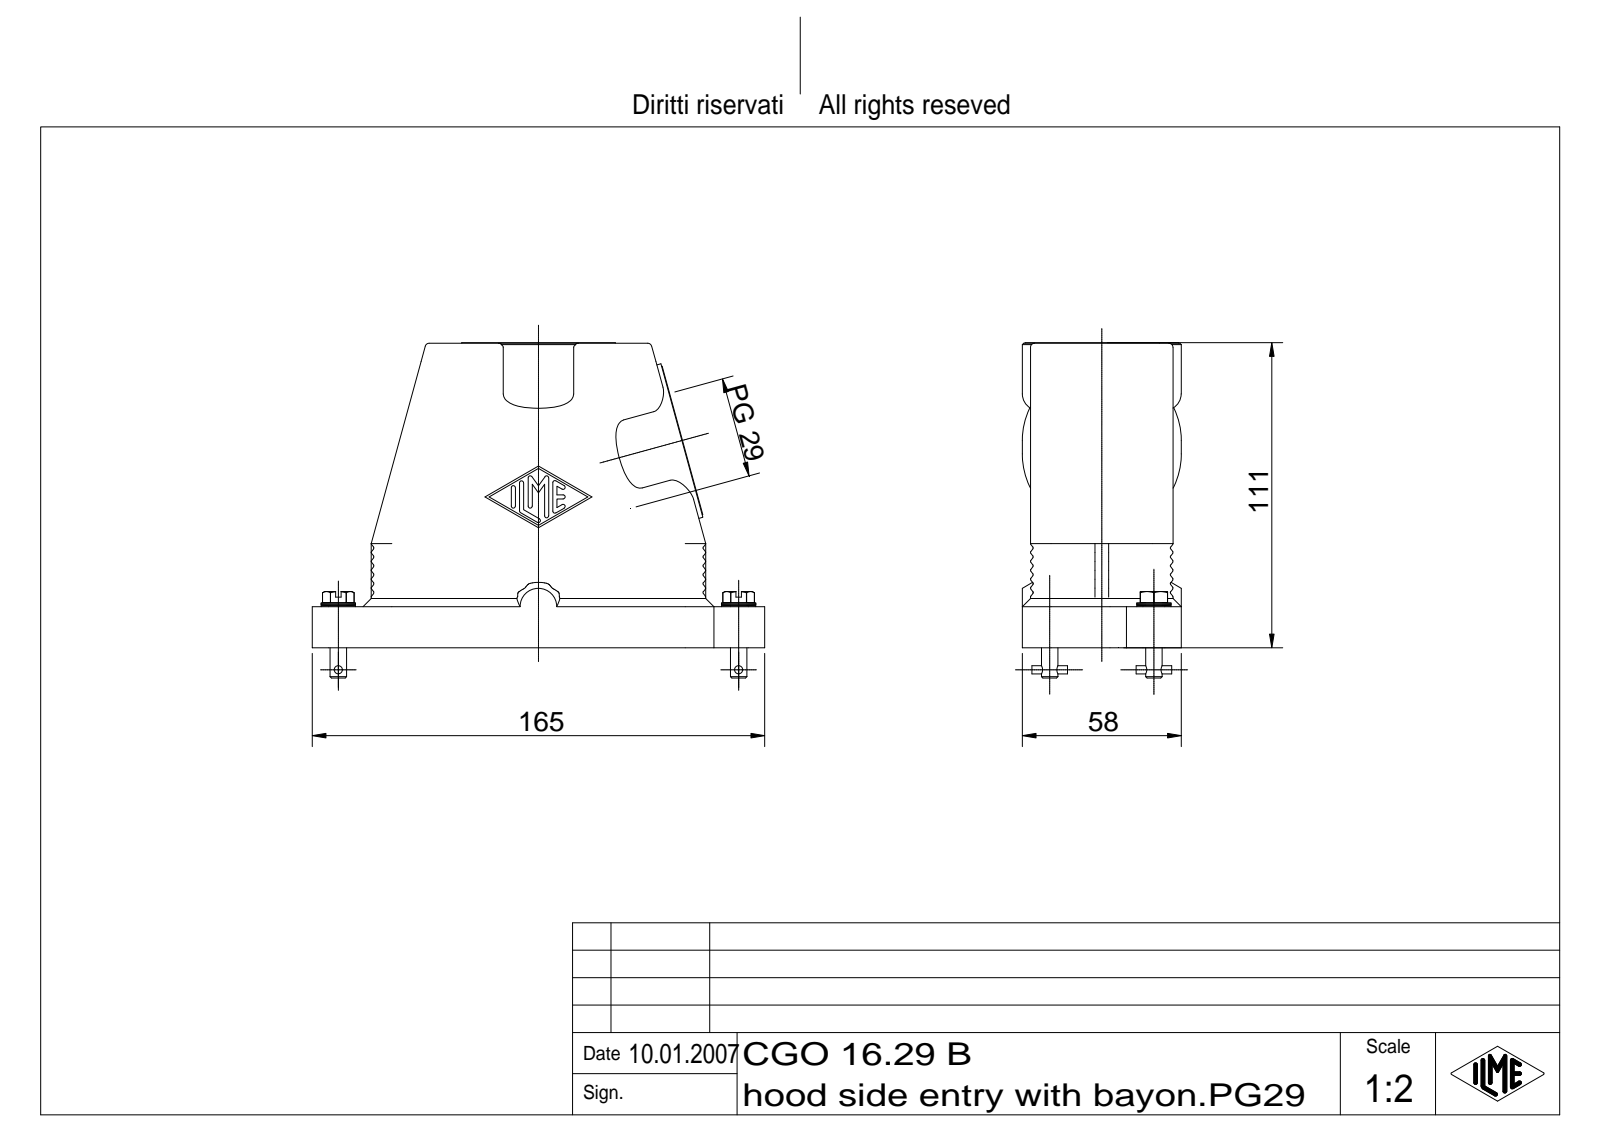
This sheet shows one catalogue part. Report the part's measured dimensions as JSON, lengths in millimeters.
{"part_name": "CGO 16.29 B", "step_written_by": "Autodesk Inventor 7 (AUTOMOTIVE_DESIGN)", "units": "millimeters", "bodies": {"solids": 3, "faces": 779, "planar": 193, "cylindrical": 203, "other": 383}, "overall_size": [165, 122.2, 58], "volume_mm3": 228050, "surface_area_mm2": 91512, "round_holes": [[2.46, 2], [3.2, 2], [6.6, 2], [15, 2], [35.48, 1]], "round_bosses_or_shafts": [[58, 2], [56, 2], [12.5, 2], [6, 2], [3, 2]], "partial_cylinders_radius": [[0.5, 39], [0.75, 14], [7.5, 8], [6, 6], [1.5, 4], [3, 4], [5.75, 2], [10.5, 2]], "face_to_face_distances": [3, 52, 49, 6, 46, 55, 2.5, 0.5, 58, 3.5], "hole_center_spacings": [34.69, 116.38, 82.07, 150.86]}
